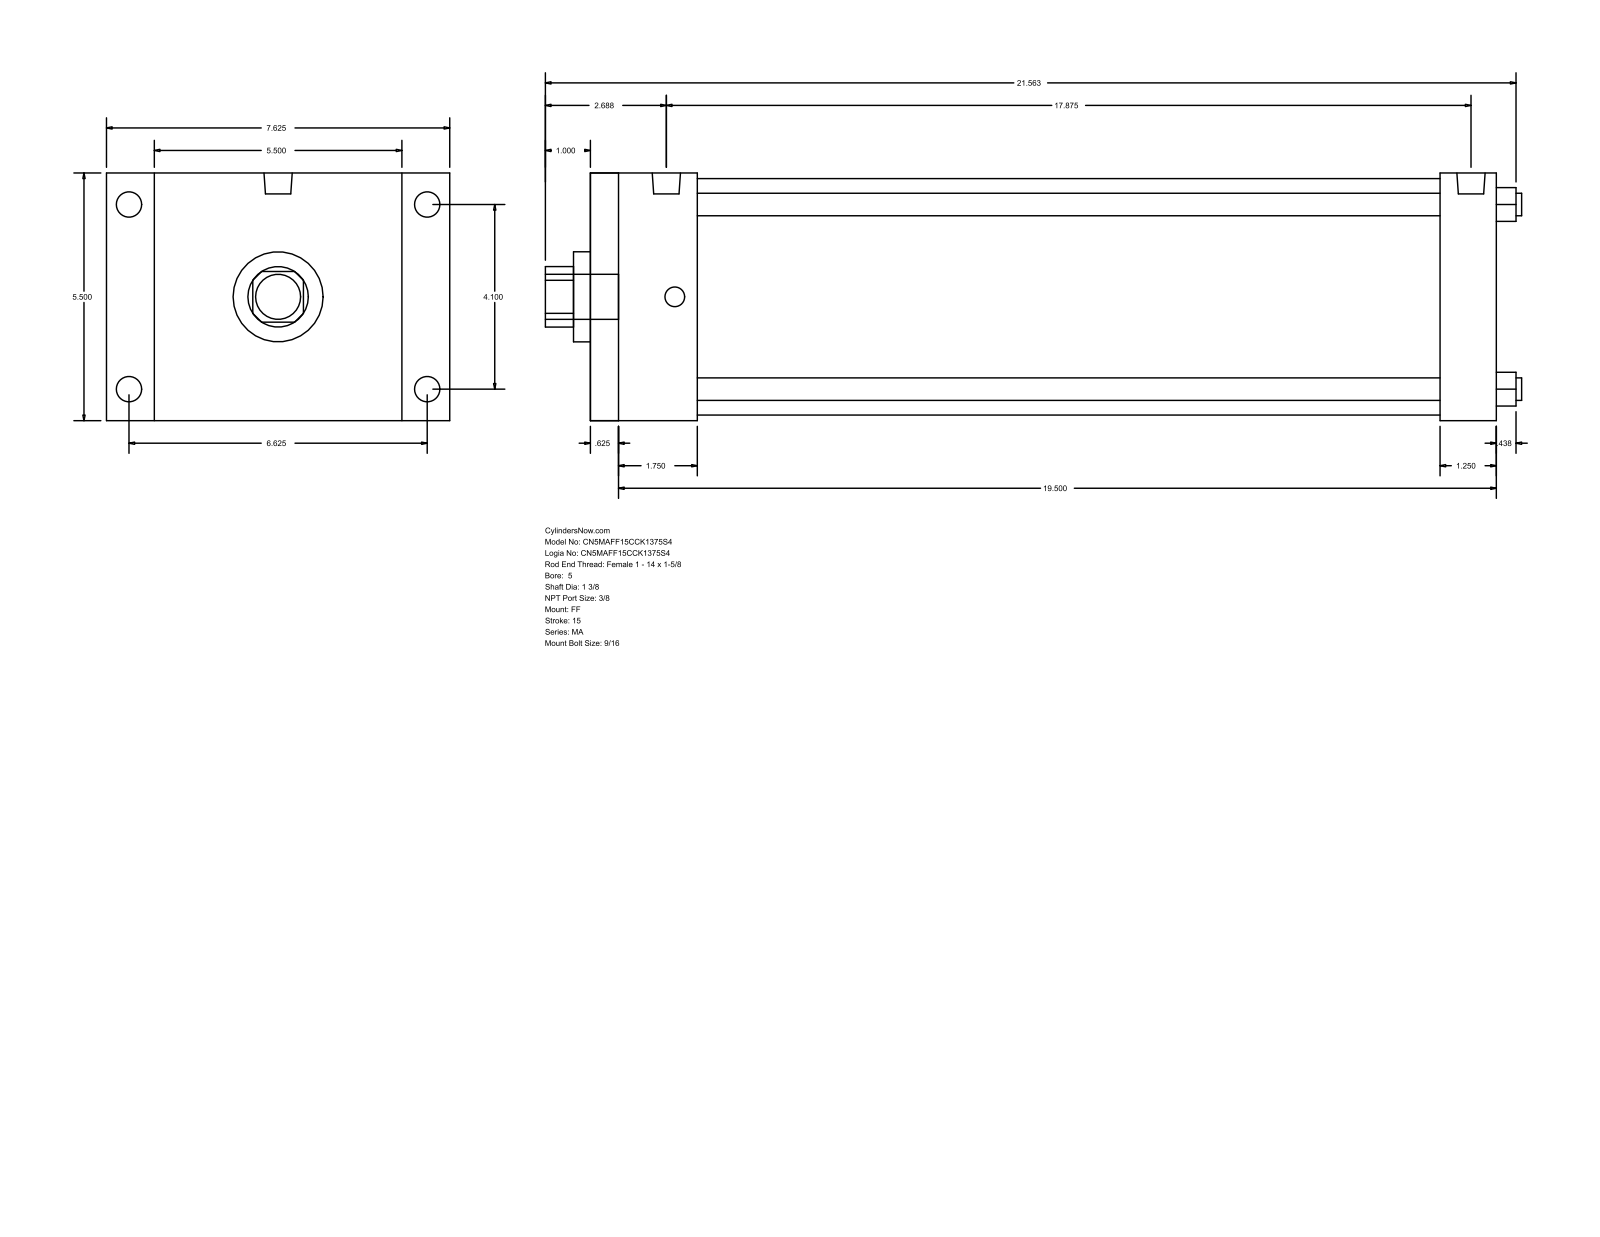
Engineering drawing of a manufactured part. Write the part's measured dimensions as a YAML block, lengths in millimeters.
part_name: "MA_FF__0500_1.375"
step_written_by: "GSSL Pune (CONFIG_CONTROL_DESIGN)"
units: millimeters
bodies: {solids: 0, faces: 92, planar: 64, cylindrical: 28, other: 0}
overall_size: [550.86, 193.68, 139.7]
round_holes:
  - {diameter: 12.7, count: 4}
  - {diameter: 34.92, count: 1}
  - {diameter: 50.8, count: 1}
  - {diameter: 133.35, count: 1}
round_bosses_or_shafts:
  - {diameter: 14.29, count: 4}
  - {diameter: 11.11, count: 4}
  - {diameter: 15.93, count: 2}
  - {diameter: 25.4, count: 1}
partial_cylinders:
  - {radius: 17.06, count: 1}
face_to_face_distances: [139.7, 511.18, 15.87, 495.31, 479.42, 463.55, 31.76, 60.32, 44.45, 419.1]
hole_center_spacings: [73.64, 104.14, 147.28]
